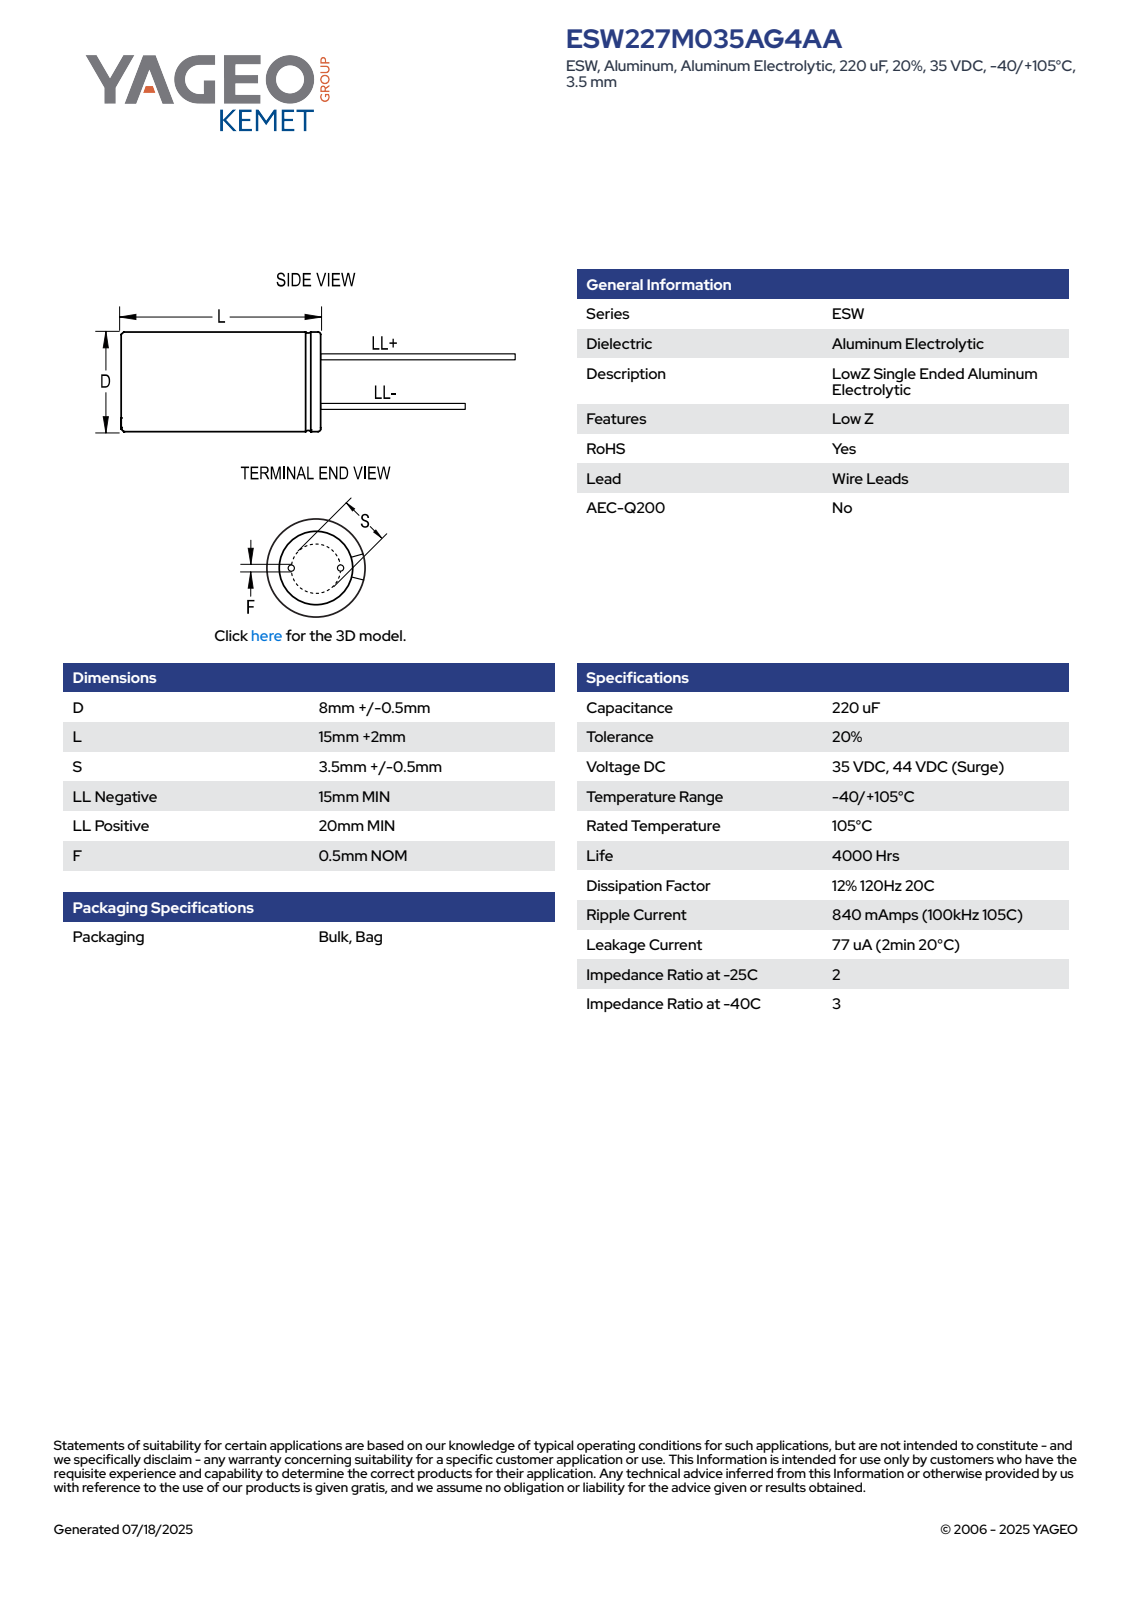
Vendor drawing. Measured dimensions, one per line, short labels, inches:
name: CAR_KLP_8X15_D8.5L17S3.5F0.5
written by: SolidWorks 2014 (AUTOMOTIVE_DESIGN)
unit: in
bodies: 4 solids, 75 faces (61 planar, 8 cylindrical, 6 other)
size: 1.457 × 0.335 × 0.335
volume: 0.059 in³; area: 0.989 in²
bosses: 2× ⌀0.02, 1× ⌀0.335
face distances: 0.669, 0.67, 1.26, 1.457, 1.26, 1.457, 0.591, 0.787, 0.197, 0.045
